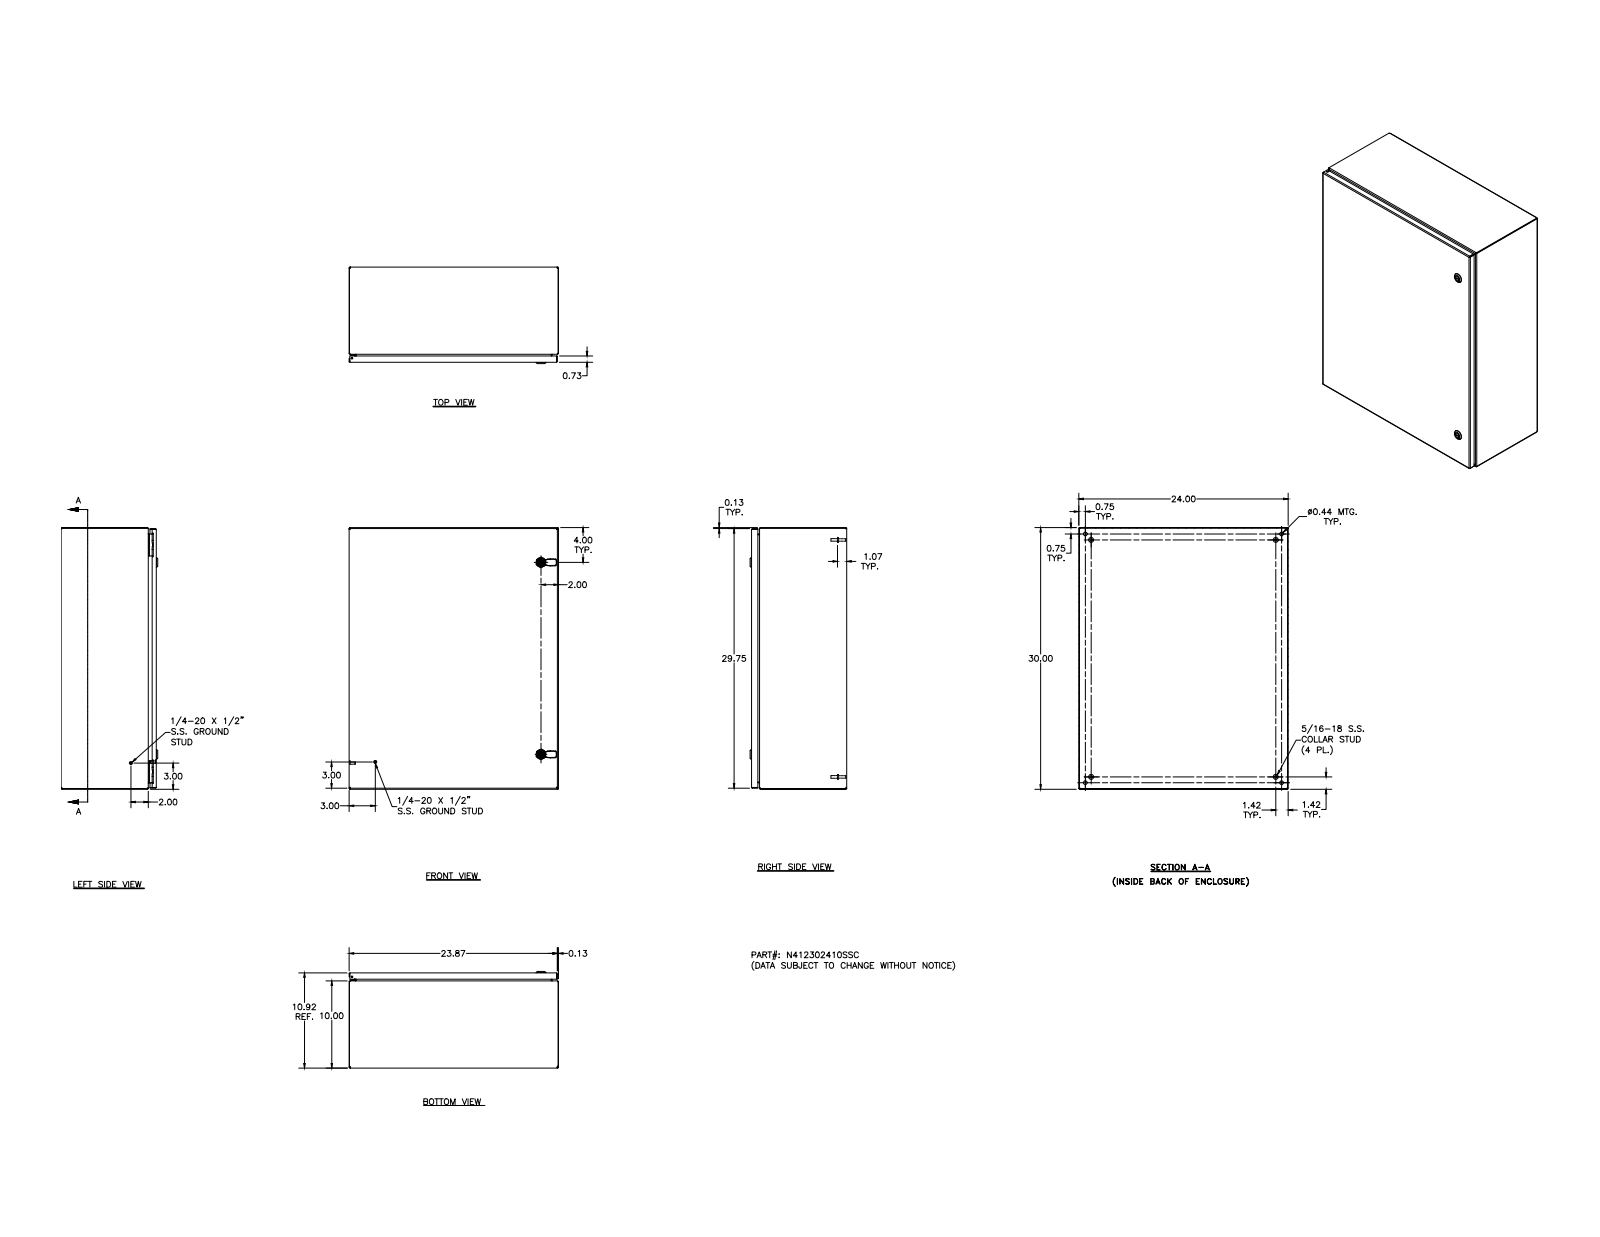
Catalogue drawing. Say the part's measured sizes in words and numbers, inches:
The part is named "N412302410SSC; N412302410SSCBKP; 388151; N4123024SSCLID (+8 more)". Its 3-D file was written by "Autodesk Inventor 2011 (AUTOMOTIVE_DESIGN)". It is 42 solids with 1682 faces: 706 planar, 600 cylindrical and 376 other. Overall it measures 30 by 24 by 11.075 inches. Its volume is 202.9 cubic inches and its surface area 5 502 square inches. Round holes: 5 of diameter 0.188, 4 of diameter 0.093, 4 of diameter 0.152, 4 of diameter 0.167, 4 of diameter 0.172, 4 of diameter 0.437, 2 of diameter 0.156, 2 of diameter 0.197, 2 of diameter 0.315, 2 of diameter 0.394, 2 of diameter 0.402, 2 of diameter 0.634. Round bosses or shafts: 10 of diameter 0.25, 4 of diameter 0.563, 4 of diameter 0.36, 4 of diameter 0.32, 4 of diameter 0.3, 4 of diameter 0.275, 4 of diameter 0.256, 4 of diameter 0.164. Partial cylindrical surfaces (rounded edges, fillets, slot ends): 30 of radius 0.031, 26 of radius 0.05, 20 of radius 0.105, 18 of radius 0.016, 15 of radius 0.02, 14 of radius 0.125, 8 of radius 0.032, 8 of radius 0.07. The main face-to-face distances are 0.074, 10.843, 10.917, 10.769, 23.926, 29.926, 23.852, 24, 29.852, 30. The hole center spacings are 26, 0.017, 0.66, 22.869, 0.019, 0.5, 0.648, 0.652.
